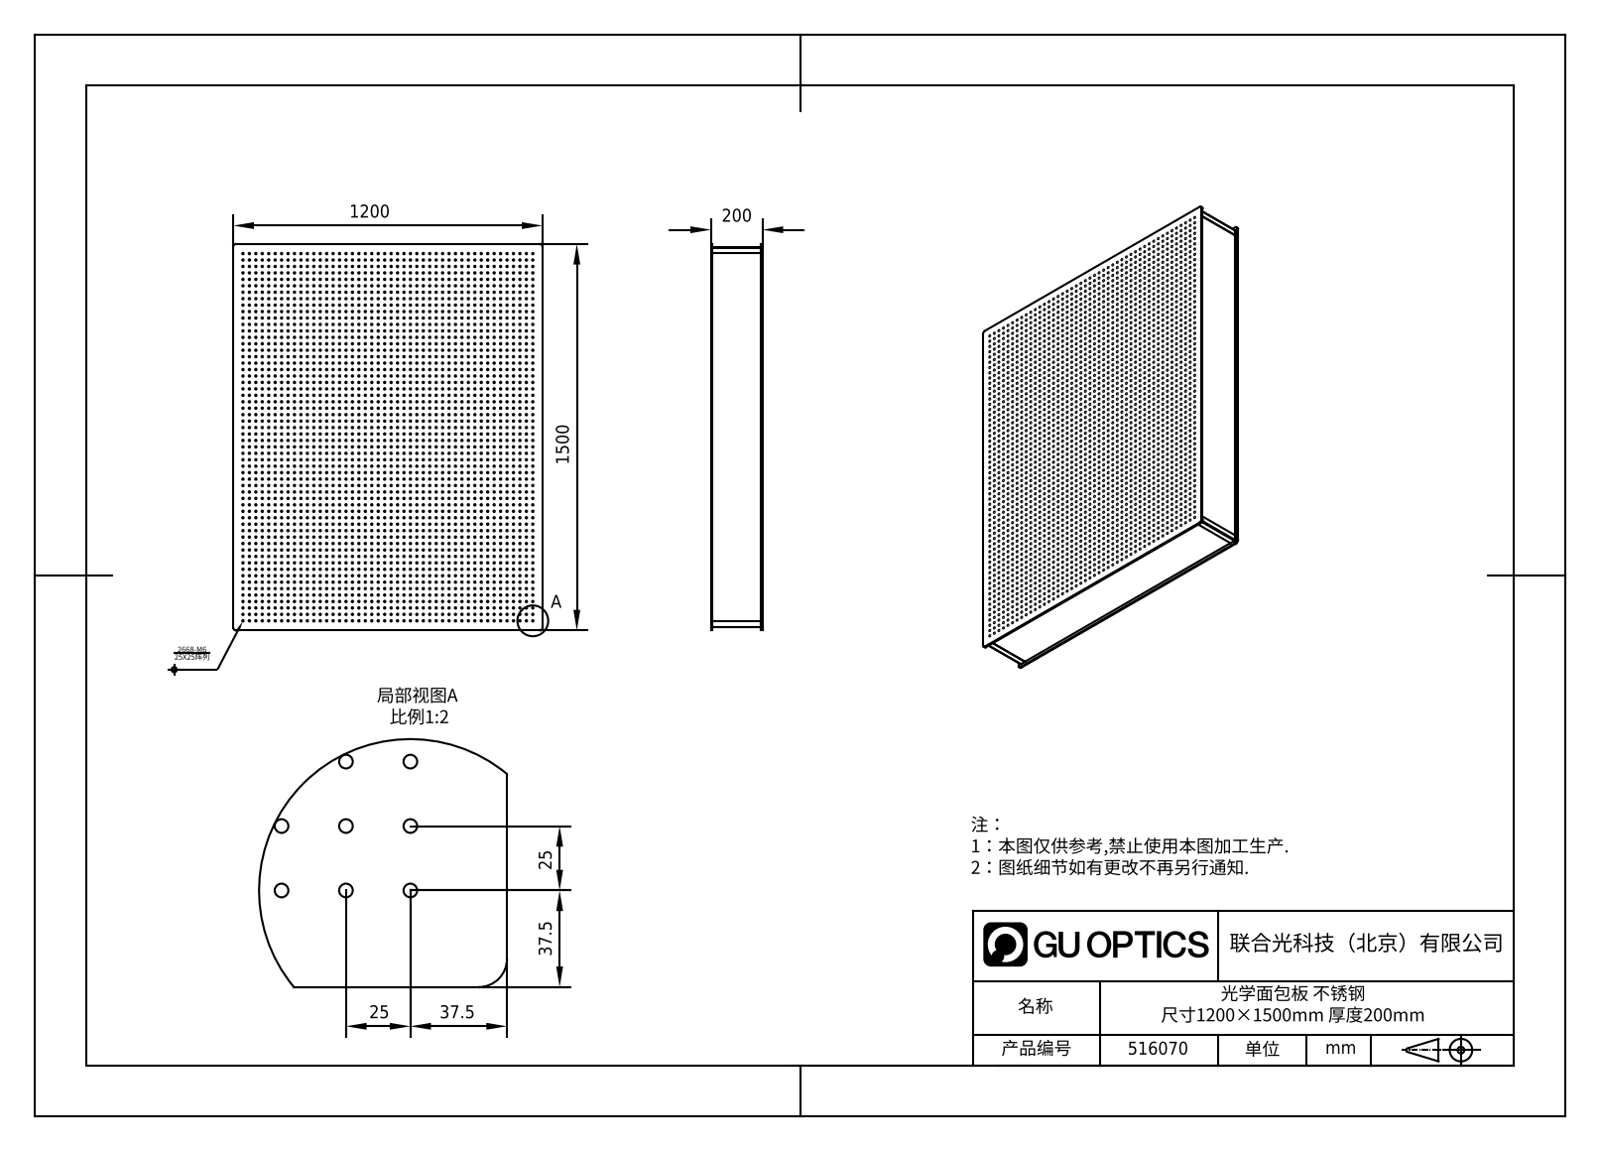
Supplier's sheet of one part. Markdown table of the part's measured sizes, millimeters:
| quantity | value |
| --- | --- |
| part name | 516070 |
| STEP written by | SolidWorks 2020 (CONFIG_CONTROL_DESIGN) |
| units | millimeters |
| bodies | 1 solid, 8064 faces (2712 planar, 5352 cylindrical, 0 other) |
| overall size | 1500 × 1200 × 200 |
| volume | 346 500 000 mm³ |
| surface area | 5 104 000 mm² |
| round holes (diameter × count) | 5.3 × 2668 |
| partial cylindrical surfaces (radius × count) | 2 × 4, 3 × 4, 11 × 4 |
| main face-to-face distances | 200, 1174, 1474, 6, 194, 195, 189, 5, 13, 1 |
| hole center spacings | 25, 50, 75, 100, 125, 150, 175, 200 |
